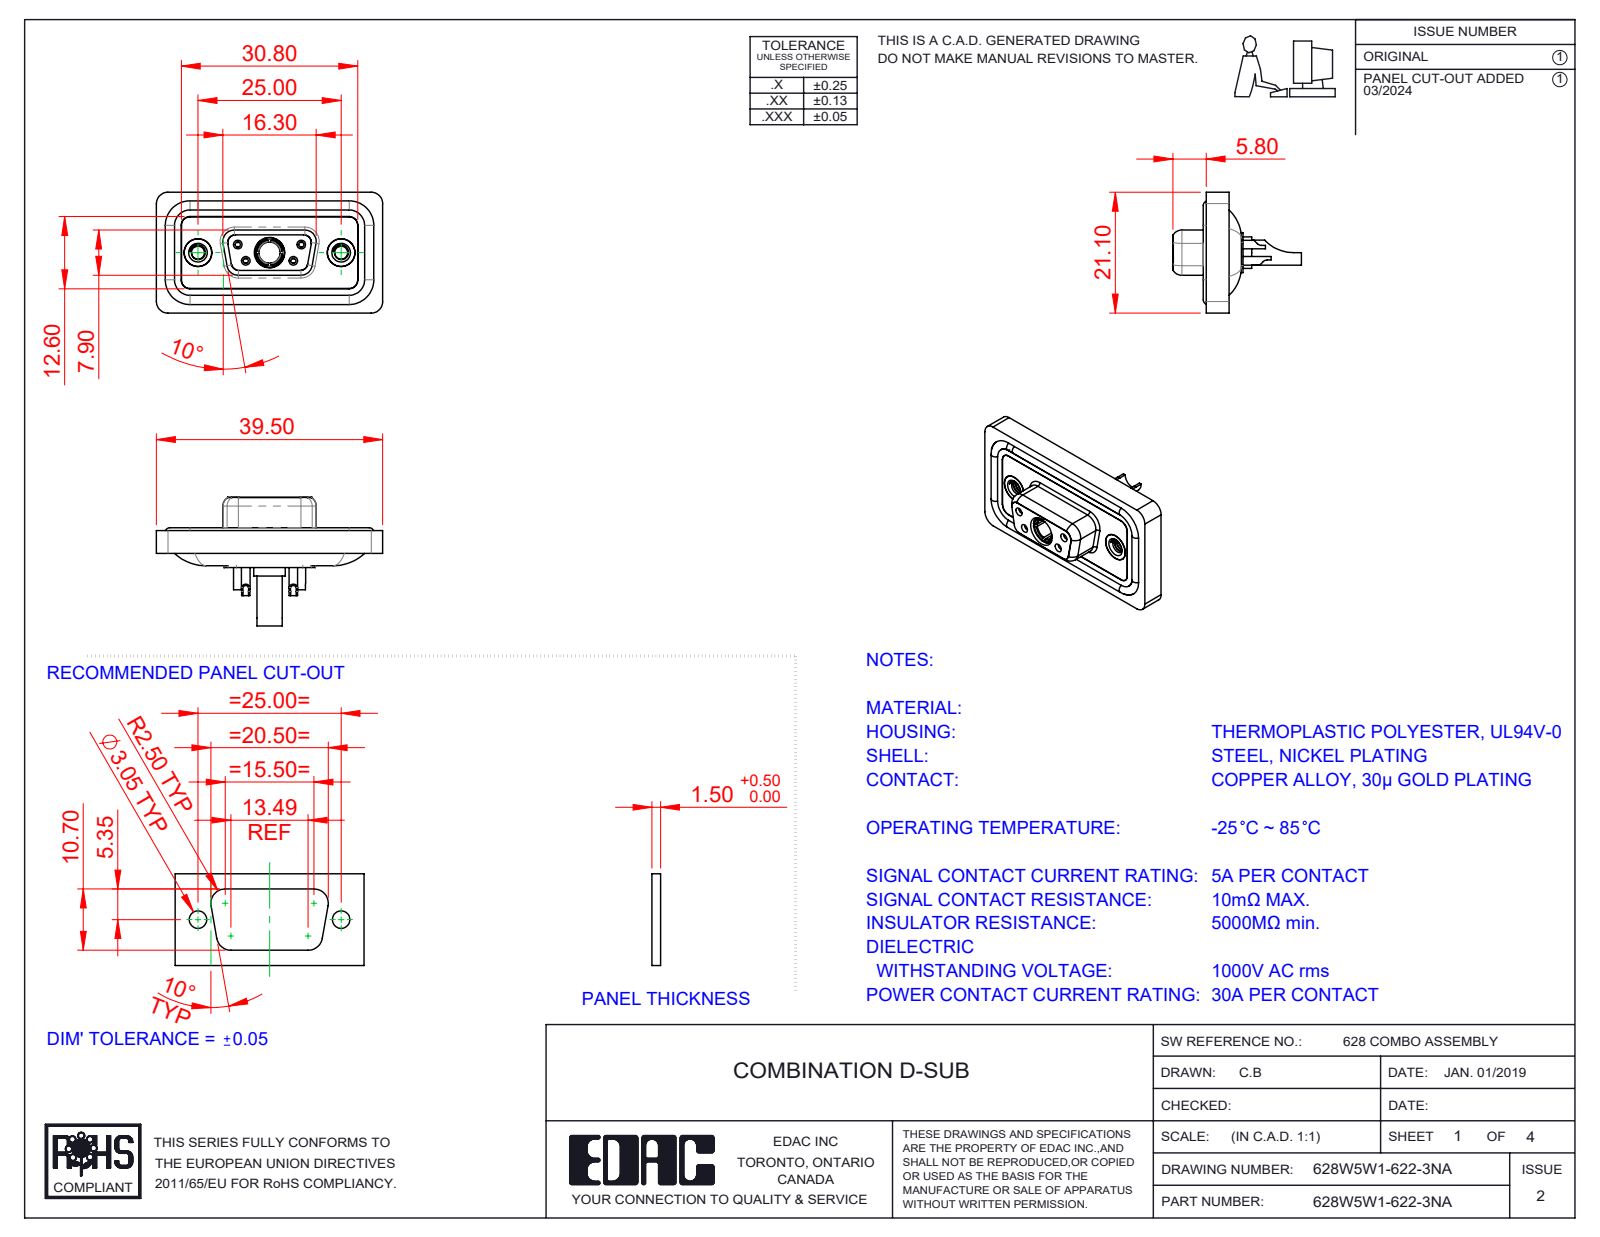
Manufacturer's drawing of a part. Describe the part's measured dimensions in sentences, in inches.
The part is named "628W5W1-622-3NA; Power Socket_30A SC; 628Combo Shell Front_09 Contacts; 628Combo Contact Row 2_22 (+5 more)". Its 3-D file was written by "SolidWorks 2023 (CONFIG_CONTROL_DESIGN)". It is 13 solids with 684 faces: 205 planar, 300 cylindrical and 179 other. Overall it measures 1.555 by 0.884 by 0.831 inches. Its volume is 0.293 cubic inches and its surface area 12.06 square inches. Round holes: 4 of diameter 0.035, 4 of diameter 0.039, 4 of diameter 0.043, 4 of diameter 0.059, 4 of diameter 0.079, 3 of diameter 0.191, 2 of diameter 0.063, 2 of diameter 0.067, 2 of diameter 0.089, 2 of diameter 0.157, 2 of diameter 0.159, 2 of diameter 0.197. Round bosses or shafts: 6 of diameter 0.063, 4 of diameter 0.087, 2 of diameter 0.195, 2 of diameter 0.189, 1 of diameter 0.217, 1 of diameter 0.205, 1 of diameter 0.195, 1 of diameter 0.187. Partial cylindrical surfaces (rounded edges, fillets, slot ends): 22 of radius 0.059, 18 of radius 0.079, 8 of radius 0.053, 8 of radius 0.063, 6 of radius 0.039, 4 of radius 0.01, 4 of radius 0.02, 4 of radius 0.024. The main face-to-face distances are 0.016, 0.114, 0.043, 0.071, 0.063, 0.02, 0.222, 0.293, 0.211, 0.142. The hole center spacings are 0.124, 0.225, 0.28, 0.492, 0.713, 0.173, 0.173, 0.327.
